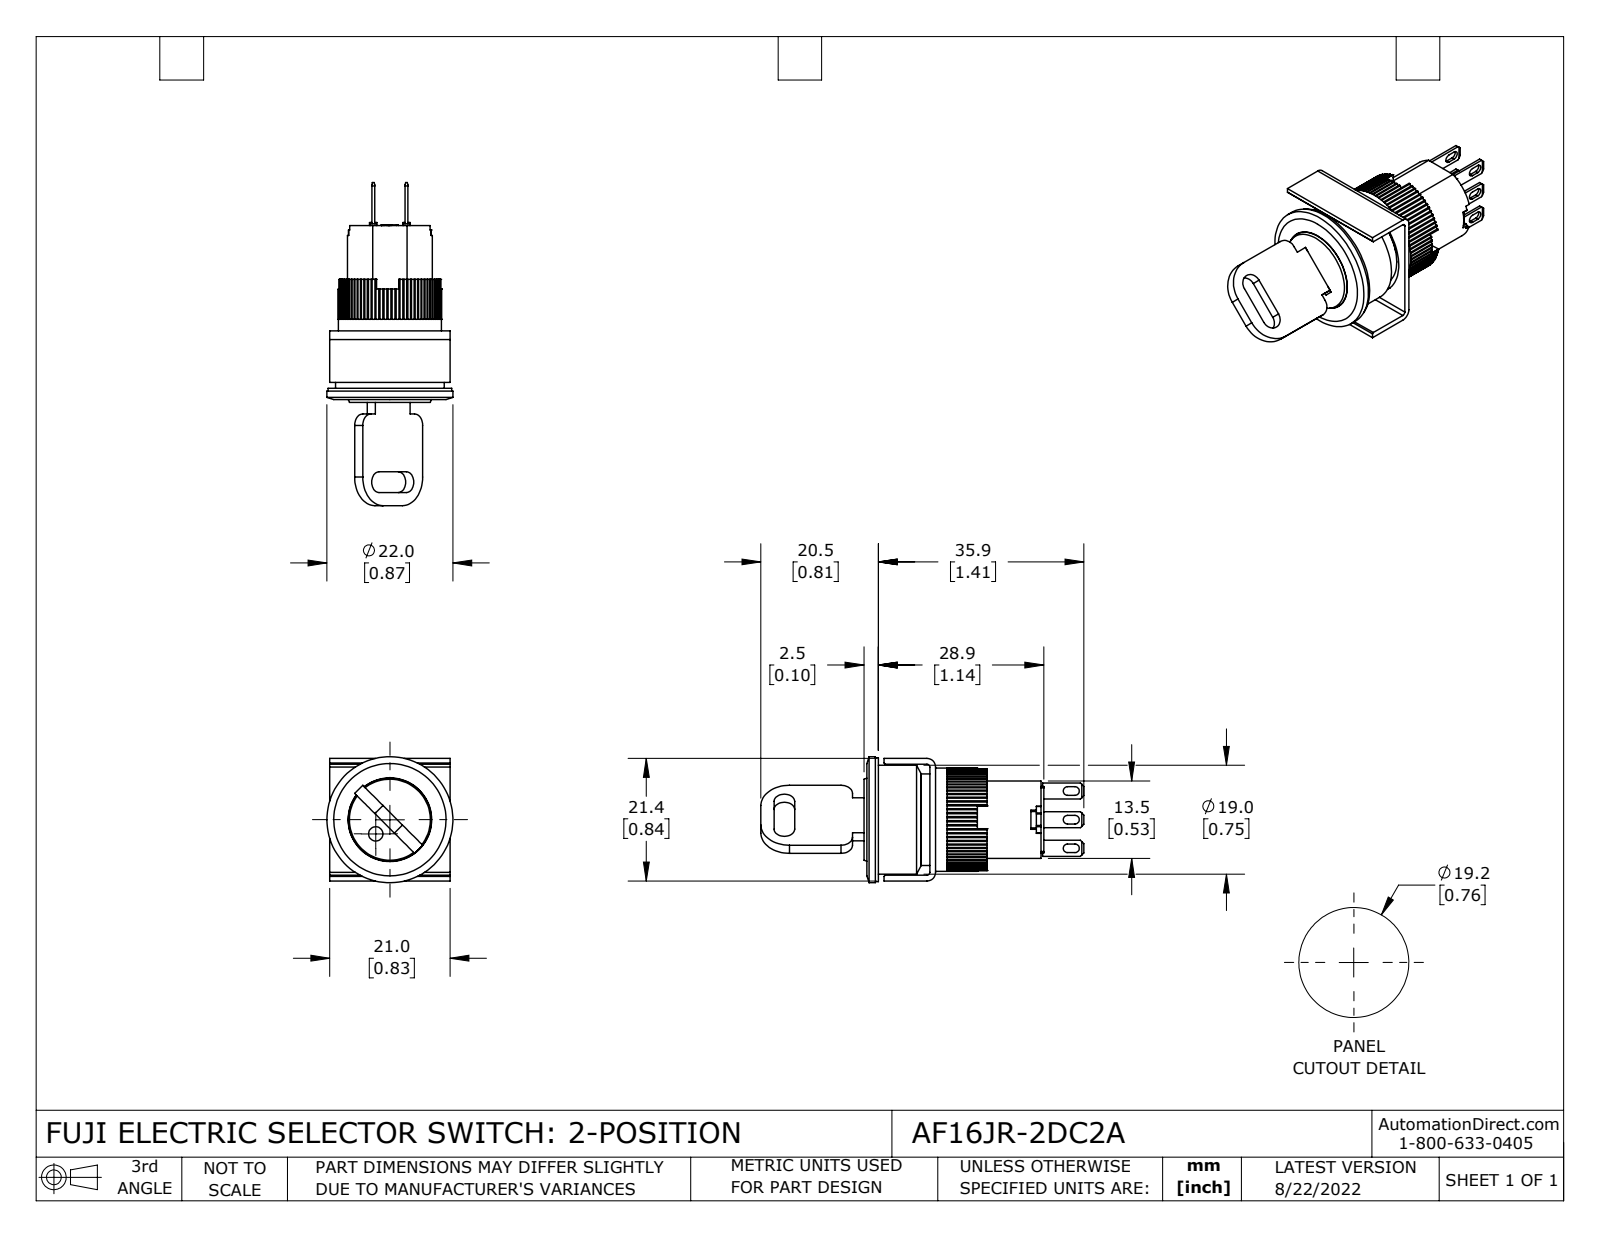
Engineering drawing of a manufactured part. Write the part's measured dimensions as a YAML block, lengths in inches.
part_name: "AF16JR-2DC2A"
step_written_by: "SolidWorks 2021 (CONFIG_CONTROL_DESIGN)"
units: inches
bodies: {solids: 13, faces: 707, planar: 518, cylindrical: 183, other: 6}
overall_size: [2.22, 0.866, 0.866]
volume: 0.495
surface_area: 11.24
round_holes:
  - {diameter: 0.039, count: 1}
  - {diameter: 0.098, count: 1}
  - {diameter: 0.575, count: 1}
  - {diameter: 0.709, count: 1}
  - {diameter: 0.748, count: 1}
round_bosses_or_shafts:
  - {diameter: 0.866, count: 1}
  - {diameter: 0.85, count: 1}
  - {diameter: 0.63, count: 1}
  - {diameter: 0.583, count: 1}
  - {diameter: 0.571, count: 1}
partial_cylinders:
  - {radius: 0.01, count: 80}
  - {radius: 0.008, count: 12}
  - {radius: 0.03, count: 6}
  - {radius: 0.02, count: 2}
  - {radius: 0.059, count: 2}
  - {radius: 0.071, count: 2}
  - {radius: 0.079, count: 2}
  - {radius: 0.197, count: 2}
face_to_face_distances: [0.079, 0.039, 0.02, 0.374, 0.177, 0.394, 0.803, 0.098, 0.059, 0.764]
hole_center_spacings: [0.137]
